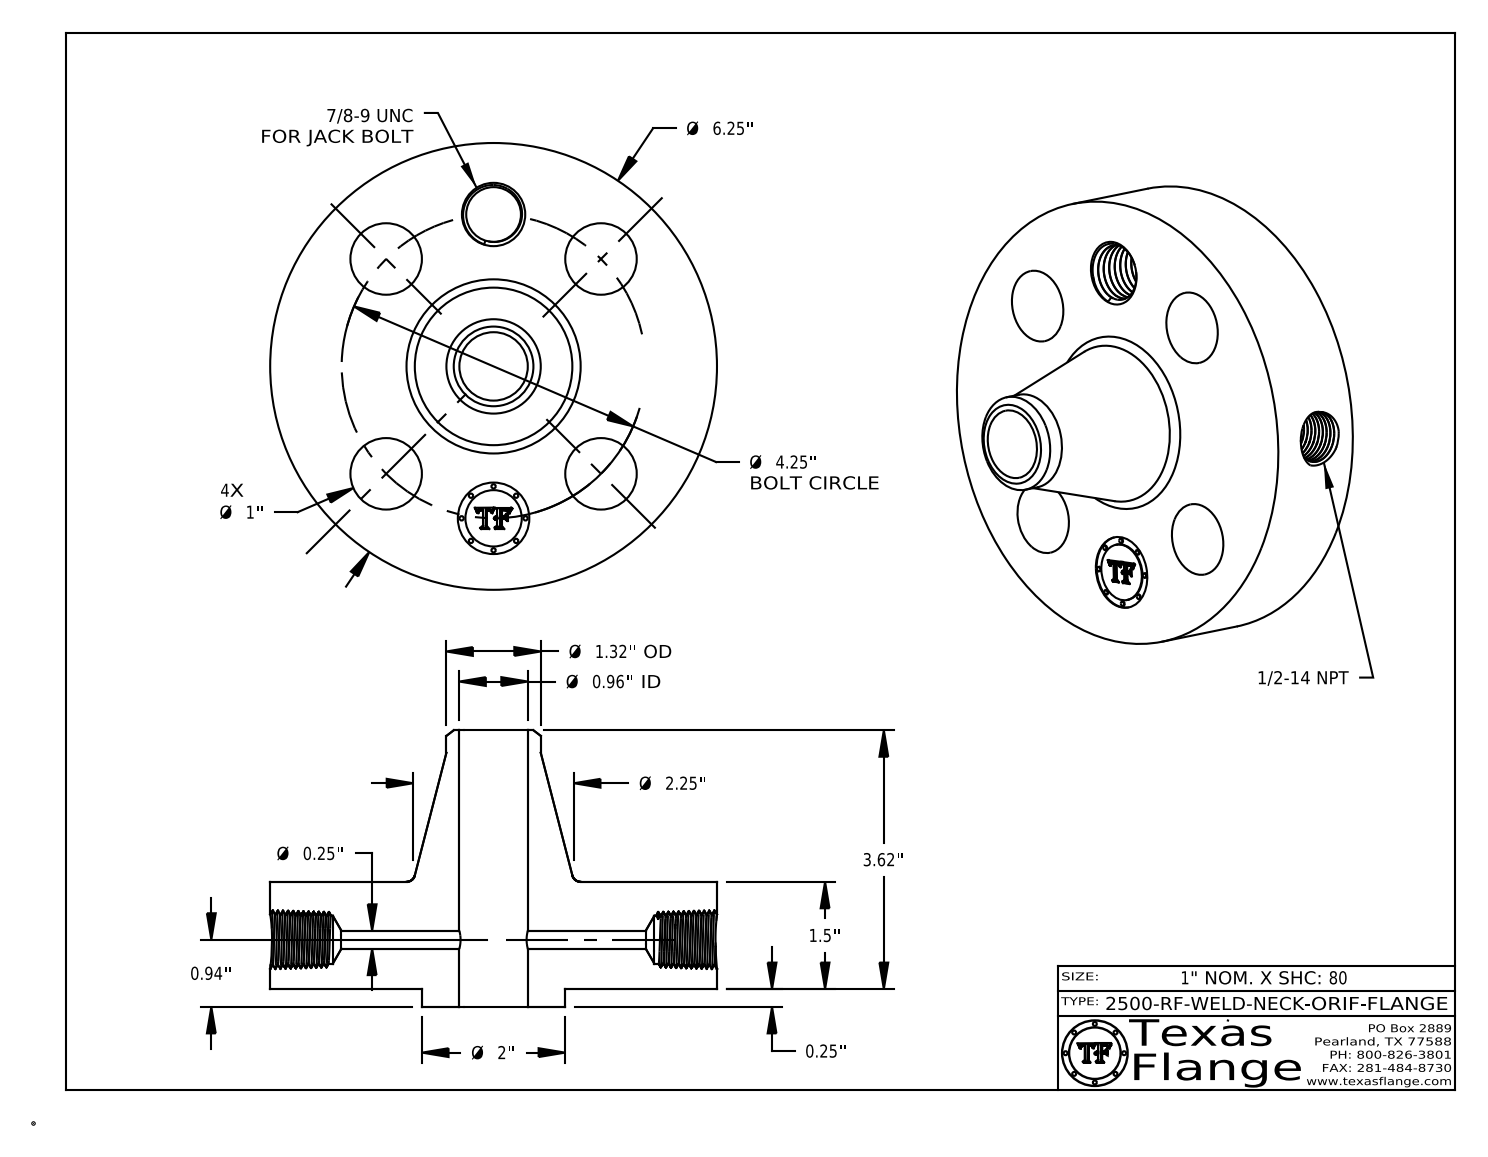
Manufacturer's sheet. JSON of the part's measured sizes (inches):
{"part_name": "2500-RF-WELD-NECK", "step_written_by": "CATIA V5 STEP AP214 (AUTOMOTIVE_DESIGN)", "units": "inches", "bodies": {"solids": 1, "faces": 751, "planar": 369, "cylindrical": 82, "other": 300}, "overall_size": [6.25, 6.25, 3.87], "volume_in3": 42.61, "surface_area_in2": 137.8, "round_holes": [[1, 5], [0.25, 1], [0.672, 1], [0.766, 1], [0.957, 1]], "round_bosses_or_shafts": [[0.061, 8], [6.25, 1], [2, 1], [1.32, 1], [0.788, 1]], "face_to_face_distances": [1.5, 0.25, 1.75, 0.015, 1.735, 1.485, 3.87, 3.62, 2.135, 2.12], "hole_center_spacings": [2.125, 1.626, 3.006, 3.927, 4.25]}
